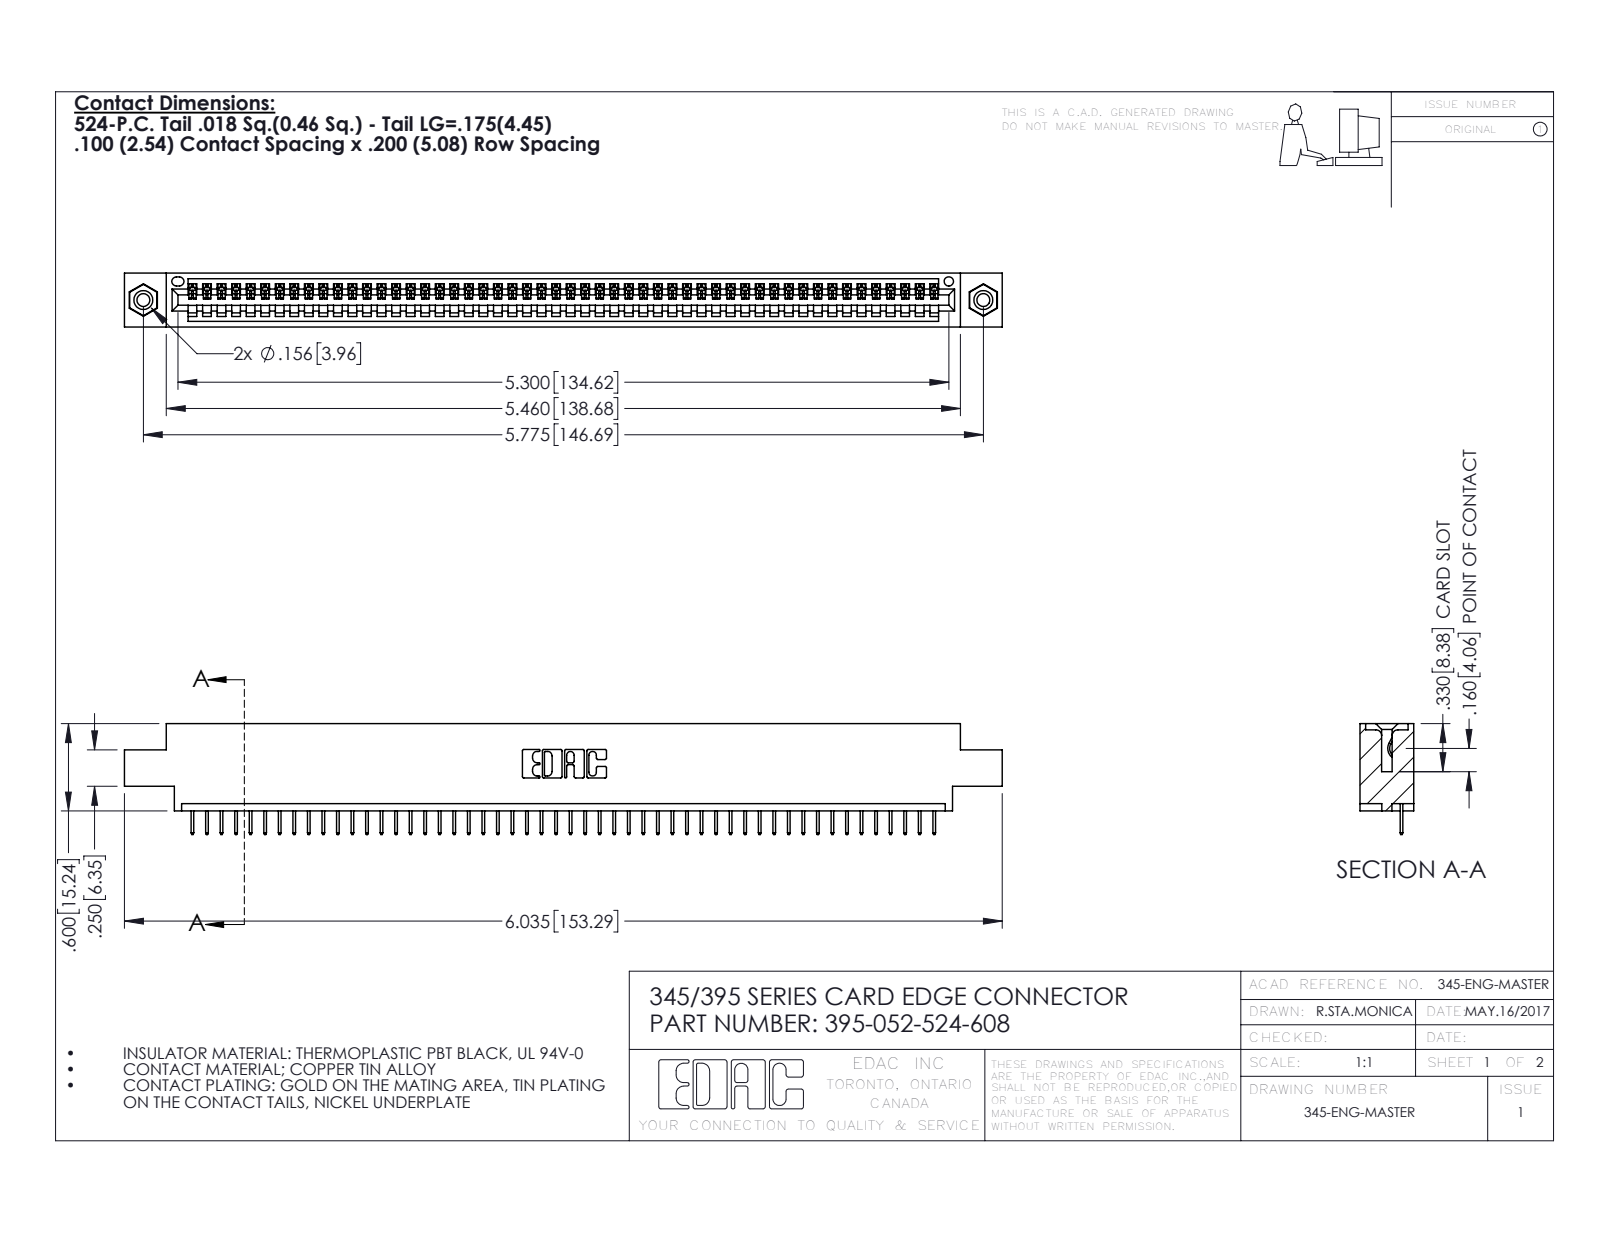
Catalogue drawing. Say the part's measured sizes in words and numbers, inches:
The part is named "345 Part_0.170 Offset - 0.156 Dia-TI; 345-292-001_345-293-124; 345-250-001_345-250-003-102; 395-052-524-608". Its 3-D file was written by "SolidWorks 2016 (CONFIG_CONTROL_DESIGN)". It is 55 solids with 3414 faces: 2508 planar, 890 cylindrical and 16 other. Overall it measures 6.035 by 0.762 by 0.37 inches. Its volume is 0.874 cubic inches and its surface area 28.91 square inches. Round holes: 2 of diameter 0.089, 2 of diameter 0.125, 2 of diameter 0.156, 1 of diameter 0.064. Round bosses or shafts: 2 of diameter 0.155. Partial cylindrical surfaces (rounded edges, fillets, slot ends): 104 of radius 0.006, 22 of radius 0.01, 6 of radius 0.007, 6 of radius 0.031, 3 of radius 0.026, 2 of radius 0.031, 2 of radius 0.04, 1 of radius 0.014. The main face-to-face distances are 0.072, 0.298, 0.37, 0.2, 0.098, 0.272, 0.025, 0.225, 0.072, 0.175. The hole center spacings are 0.27, 5.539, 5.775.
